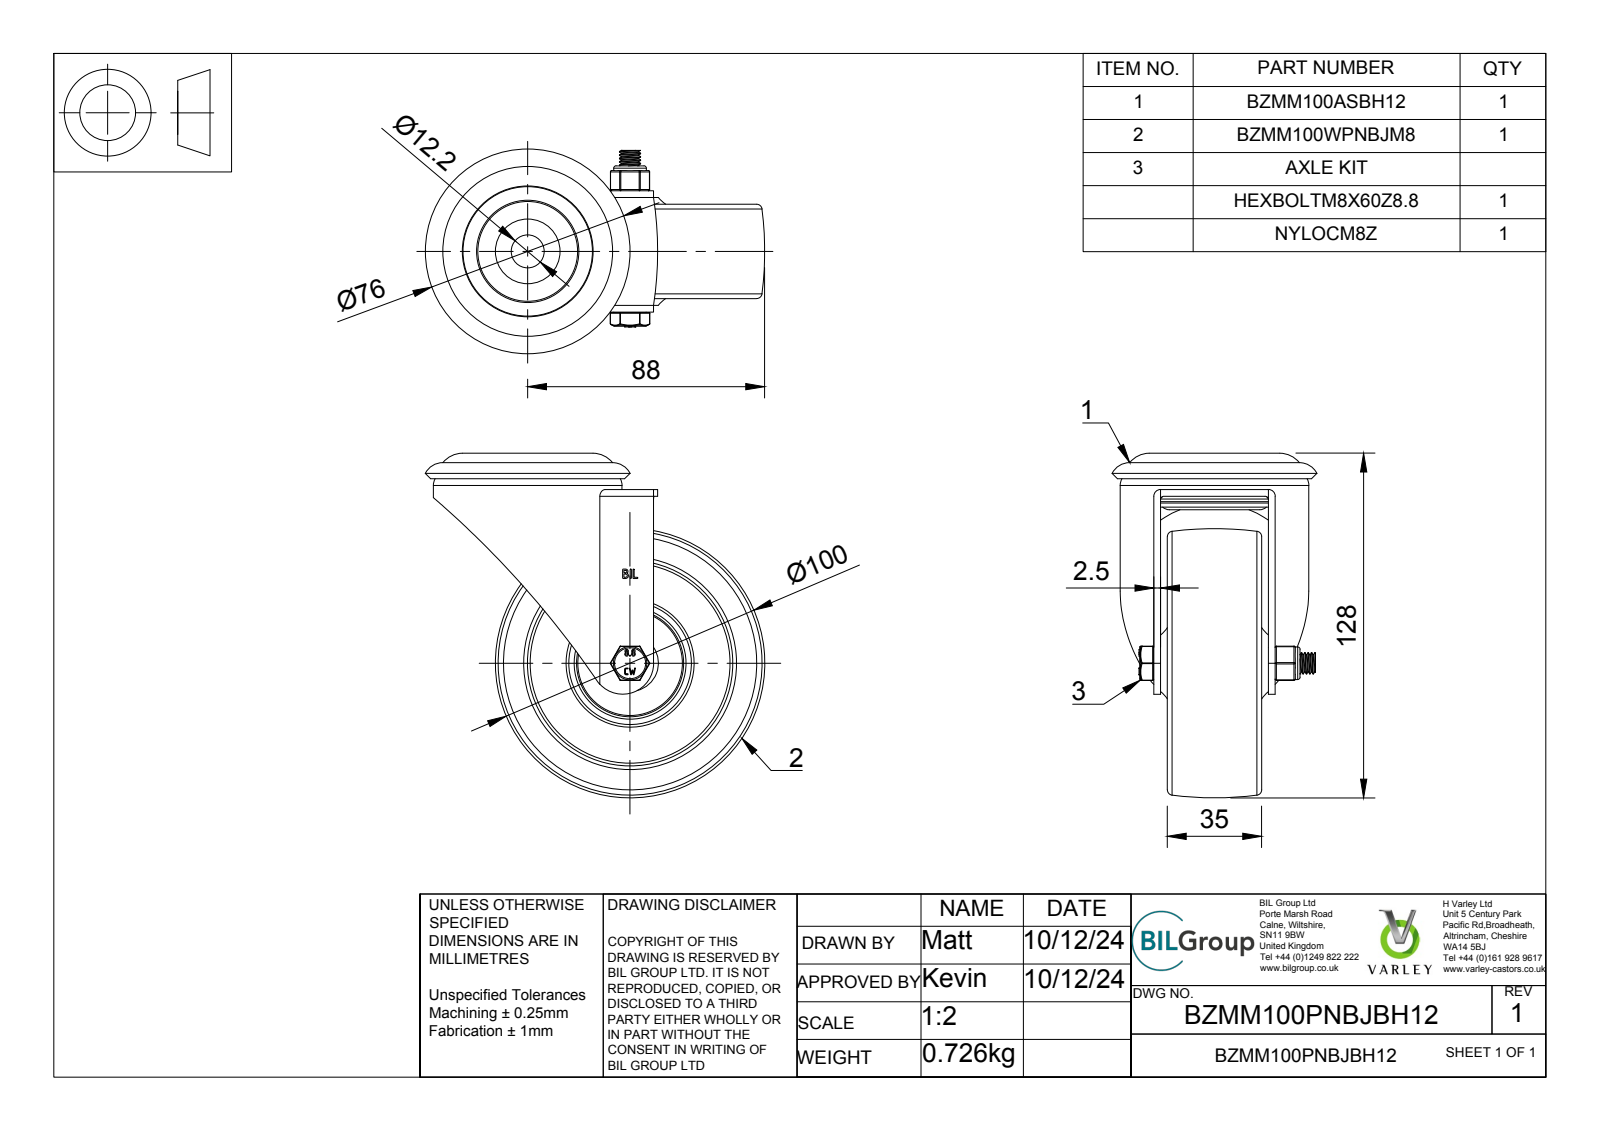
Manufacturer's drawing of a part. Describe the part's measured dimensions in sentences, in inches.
The part is named "BZMM100PNBJBH12 v3; BZMM100ASBH12 v1; ZINC PLATED PRESSED STEEL HEAD; ZINC PLATED, PRESSED STEEL FORKS (+7 more)". Its 3-D file was written by "Autodesk Translation Framework v13.20.0.188 (AP242_MANAGED_MODEL_BASED_3D_ENGINEERING_MIM_LF)". It is 22 solids with 775 faces: 303 planar, 186 cylindrical and 286 other. Overall it measures 5.039 by 4.961 by 2.992 inches. Its volume is 13.27 cubic inches and its surface area 198.8 square inches. Round holes: 2 of diameter 0.026, 1 of diameter 0.315, 1 of diameter 0.323, 1 of diameter 0.331, 1 of diameter 0.339, 1 of diameter 0.48, 1 of diameter 0.591, 1 of diameter 0.787, 1 of diameter 0.886, 1 of diameter 1.024, 1 of diameter 1.181, 1 of diameter 1.22. Round bosses or shafts: 1 of diameter 2.756, 1 of diameter 1.949, 1 of diameter 1.791, 1 of diameter 1.565, 1 of diameter 1.496, 1 of diameter 1.457, 1 of diameter 1.201, 1 of diameter 0.945. Partial cylindrical surfaces (rounded edges, fillets, slot ends): 18 of radius 0.02, 12 of radius 0.01, 4 of radius 0.013, 4 of radius 0.025, 4 of radius 0.049, 2 of radius 0.025, 2 of radius 0.025, 2 of radius 0.098. The main face-to-face distances are 0.098, 0.787, 0.472, 0.197, 0.669, 0.118, 0.591, 1.575, 0.315, 0.984. The hole center spacings are 0.183, 0.098.
